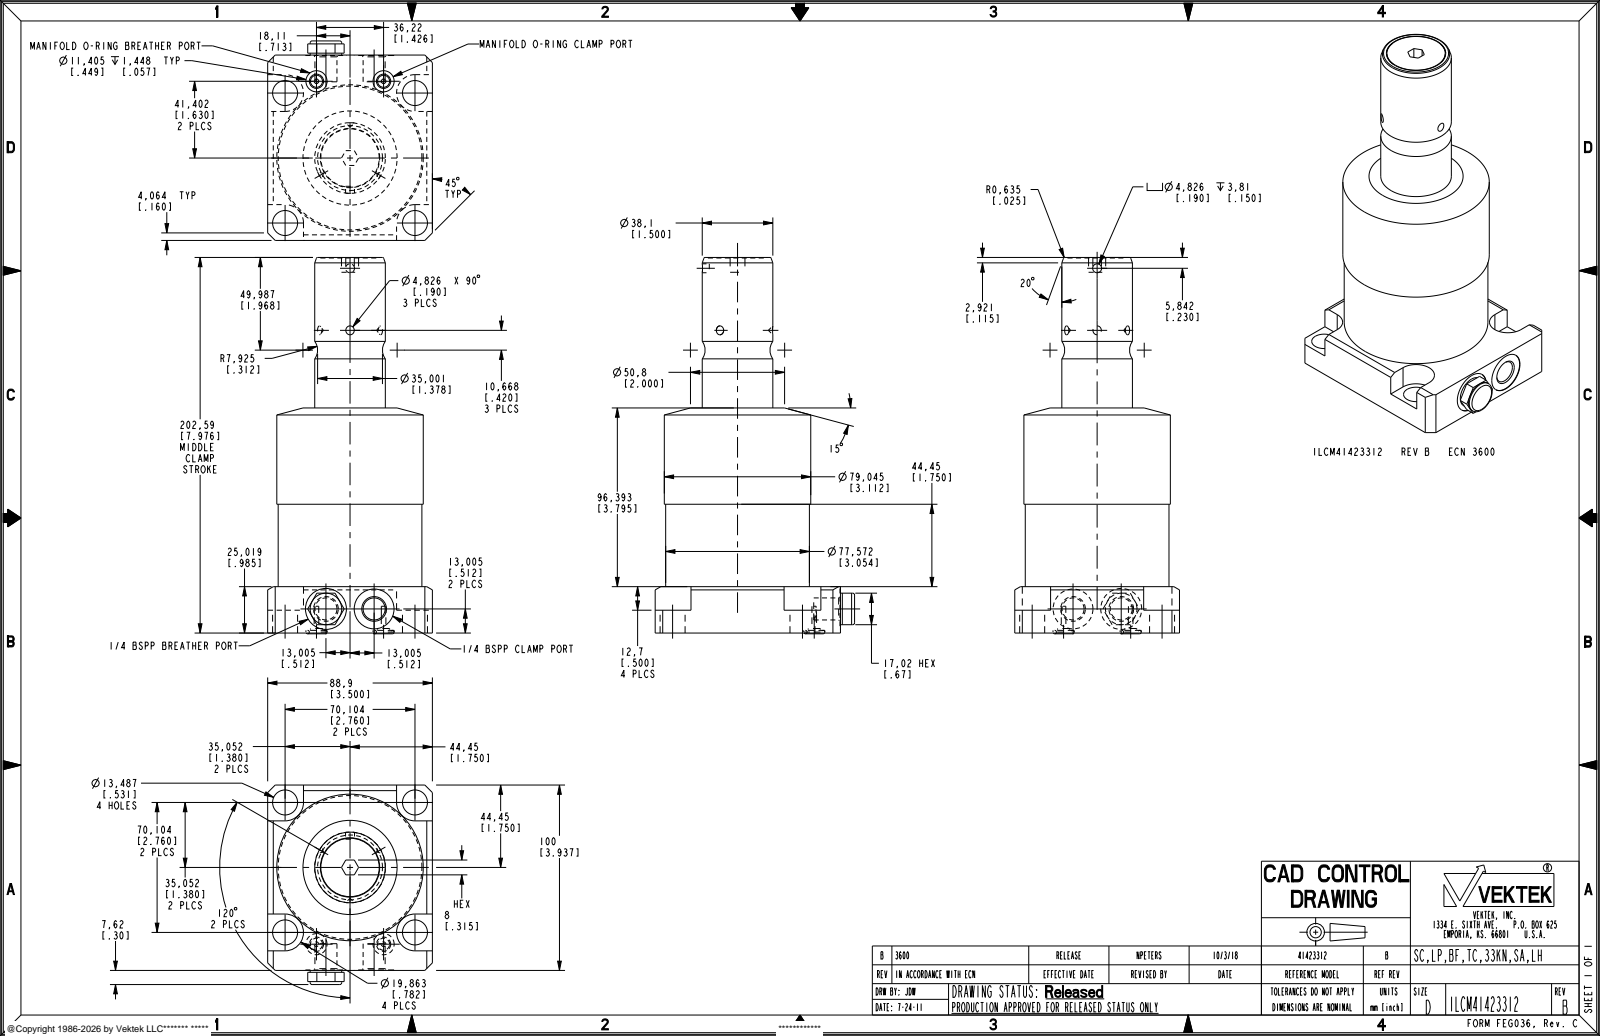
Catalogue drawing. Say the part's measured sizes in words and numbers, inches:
The part is named "ILCM41423312". Its 3-D file was written by "PRO/ENGINEER BY PARAMETRIC TECHNOLOGY CORPORATION, 2013320 (AUTOMOTIVE_DESIGN)". It is 1 solid with 150 faces: 70 planar, 52 cylindrical and 28 other. Overall it measures 7.992 by 4.237 by 3.5 inches. Its volume is 45.45 cubic inches and its surface area 99.2 square inches. Round holes: 4 of diameter 0.531, 2 of diameter 0.098, 2 of diameter 0.256, 2 of diameter 0.449, 2 of diameter 0.468, 1 of diameter 0.19, 1 of diameter 0.846, 1 of diameter 0.87, 1 of diameter 1.26. Round bosses or shafts: 1 of diameter 3.112, 1 of diameter 3.054, 1 of diameter 1.5, 1 of diameter 1.24, 1 of diameter 0.67. Partial cylindrical surfaces (rounded edges, fillets, slot ends): 4 of radius 0.391. The main face-to-face distances are 0.985, 3.5, 3.937, 3.795, 4.78, 3.196, 6.991, 7.976, 7.491, 4.295. The hole center spacings are 1.952, 2.76, 0.712, 1.779, 2.108, 3.083, 3.666, 3.903.
